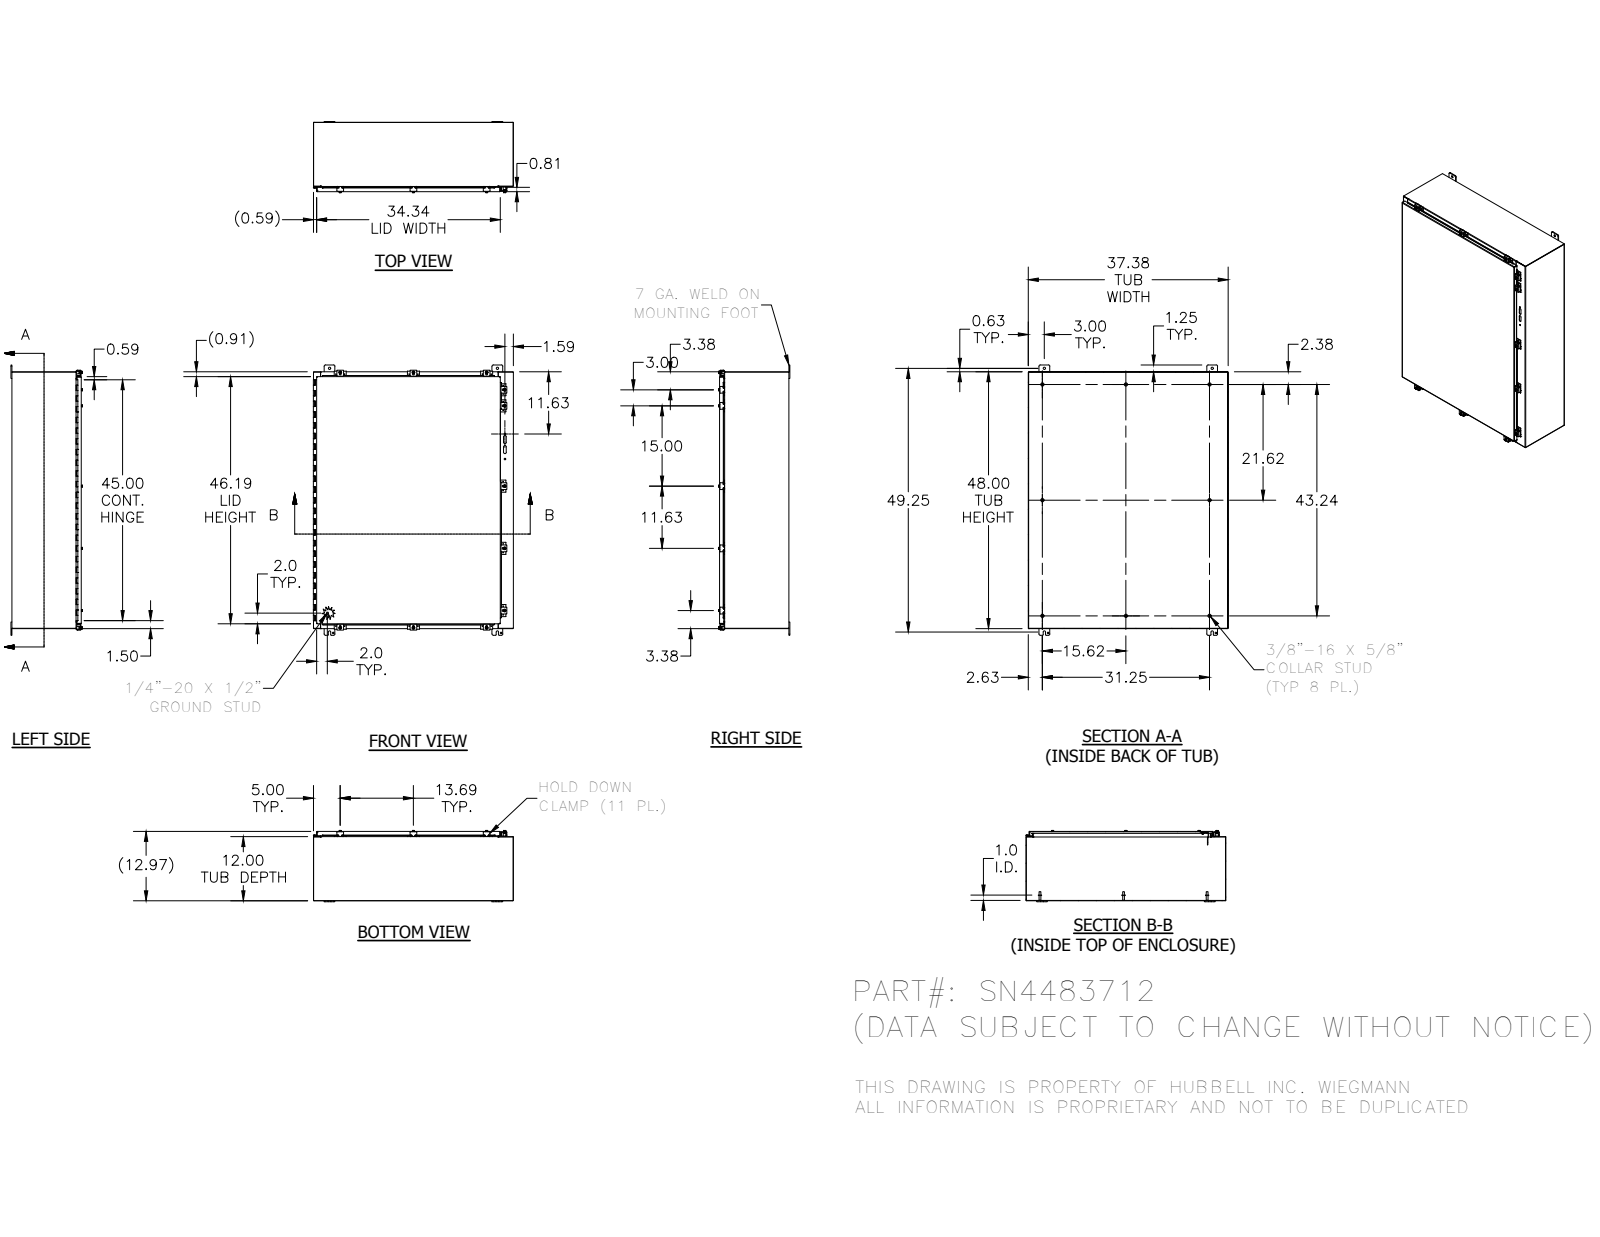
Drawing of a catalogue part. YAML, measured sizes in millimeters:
part_name: "SN4483712BLR; 3889; 34840; 328115T (+8 more)"
step_written_by: "Autodesk Inventor 2016 (AUTOMOTIVE_DESIGN)"
units: millimeters
bodies: {solids: 80, faces: 2330, planar: 1258, cylindrical: 758, other: 314}
overall_size: [1282.7, 949.74, 338.45]
volume: 7477000
surface_area: 7974000
round_holes:
  - {diameter: 2.79, count: 22}
  - {diameter: 7.14, count: 13}
  - {diameter: 5.36, count: 11}
  - {diameter: 7.62, count: 11}
  - {diameter: 7.95, count: 4}
  - {diameter: 11.13, count: 4}
  - {diameter: 3.96, count: 2}
  - {diameter: 3.17, count: 1}
round_bosses_or_shafts:
  - {diameter: 6.35, count: 15}
  - {diameter: 13.21, count: 11}
  - {diameter: 12.7, count: 11}
  - {diameter: 8.89, count: 11}
  - {diameter: 8.38, count: 9}
  - {diameter: 15.88, count: 8}
  - {diameter: 4.83, count: 2}
  - {diameter: 8.56, count: 1}
partial_cylinders:
  - {radius: 0.76, count: 127}
  - {radius: 6.35, count: 39}
  - {radius: 3.17, count: 34}
  - {radius: 1.59, count: 23}
  - {radius: 3.57, count: 22}
  - {radius: 0.79, count: 21}
  - {radius: 2.67, count: 21}
  - {radius: 2.54, count: 16}
face_to_face_distances: [1.88, 327.59, 325.71, 329.47, 947.45, 1217.32, 949.33, 945.57, 302.92, 24.67]
hole_center_spacings: [1204.5, 22.26, 347.66, 368.39, 1245.49, 1247.93, 1259.38, 327.14]
